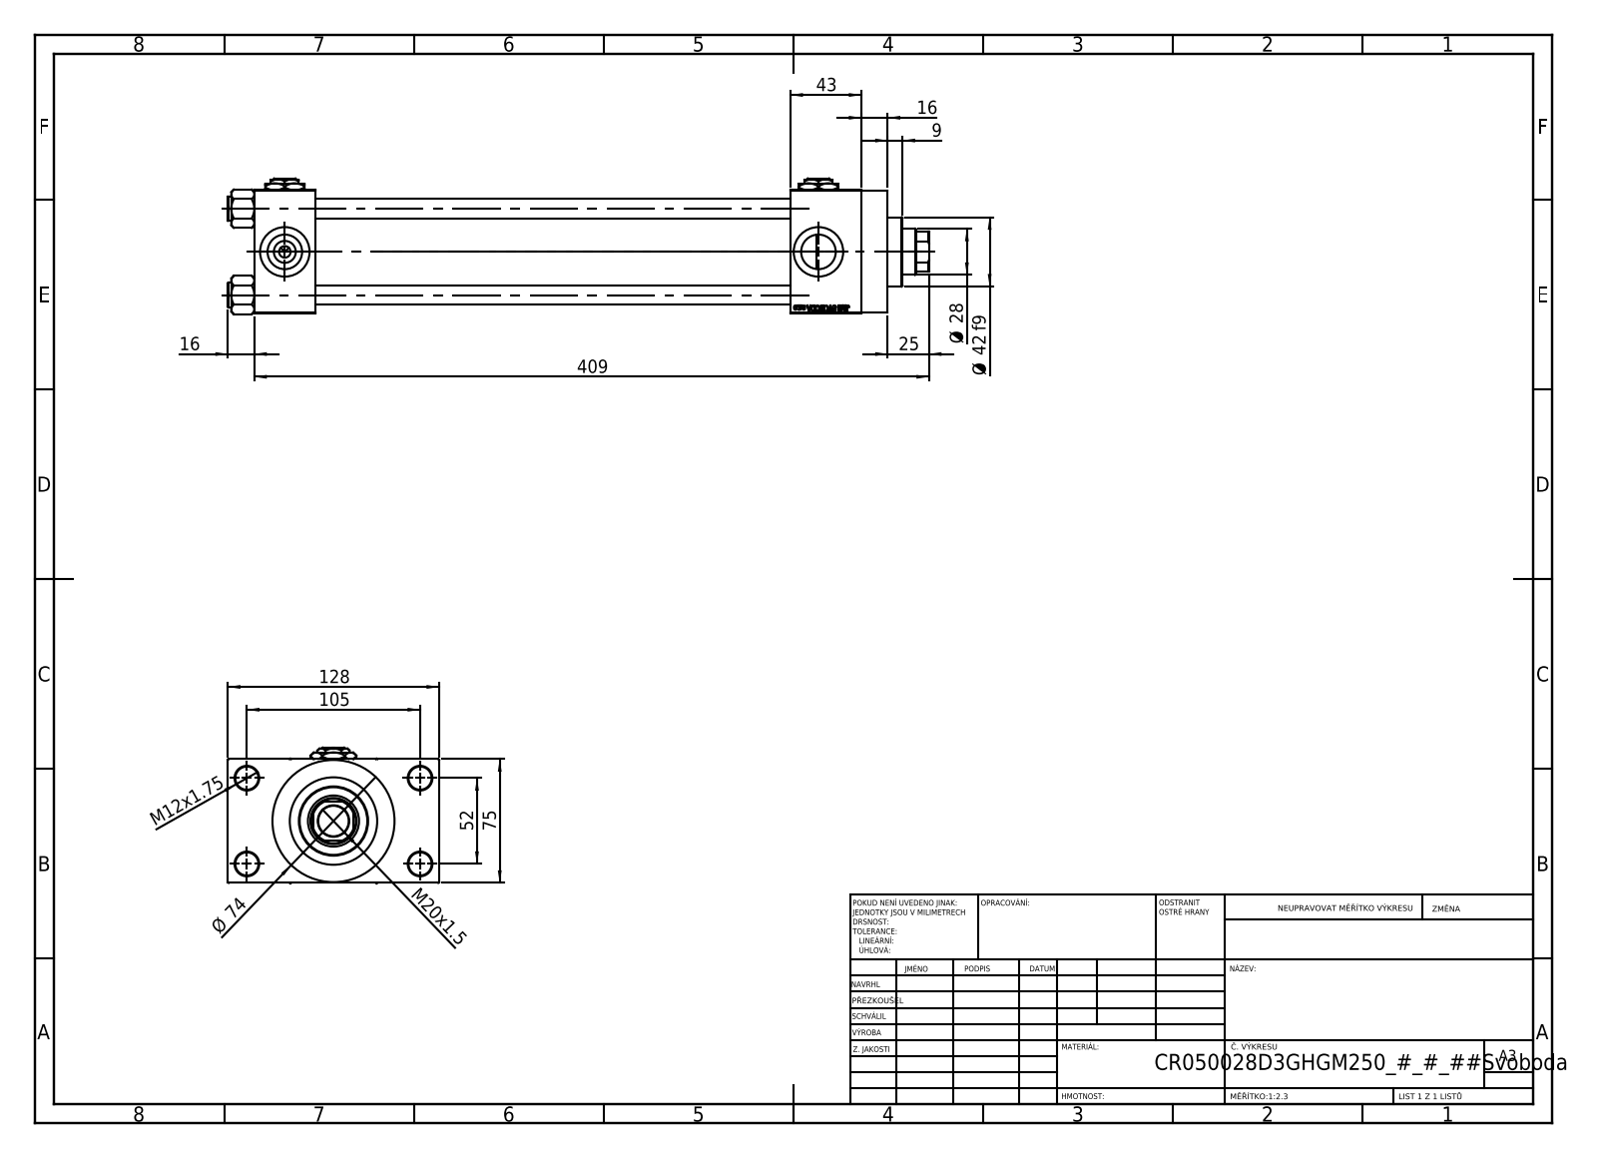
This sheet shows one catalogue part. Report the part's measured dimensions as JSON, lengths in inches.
{"part_name": "Zatka_pro_OIL_PORT; NUT_M5_D; V215CR_VCP_D; V215_VC_A (+2 more)", "step_written_by": "SolidWorks 2019 (CONFIG_CONTROL_DESIGN)", "units": "inches", "bodies": {"solids": 13, "faces": 1204, "planar": 545, "cylindrical": 99, "other": 560}, "overall_size": [16.732, 5.039, 3.239], "volume_in3": 70.91, "surface_area_in2": 474.8, "round_holes": [[0.472, 4], [0.551, 4], [0.825, 4], [1.181, 4], [0.276, 3], [0.728, 1], [1.102, 1], [1.22, 1], [1.614, 1], [1.969, 1], [2.087, 1]], "round_bosses_or_shafts": [[0.591, 4], [2.913, 1], [2.205, 1], [1.654, 1]], "partial_cylinders_radius": [[0.531, 1]], "face_to_face_distances": [2.953, 11.339, 1.457, 12.795, 1.043, 14.488, 13.031, 1.693, 3.996, 0.63], "hole_center_spacings": [1.037, 1.456, 2.059, 2.3, 2.307, 3.096, 3.715, 2.047]}
